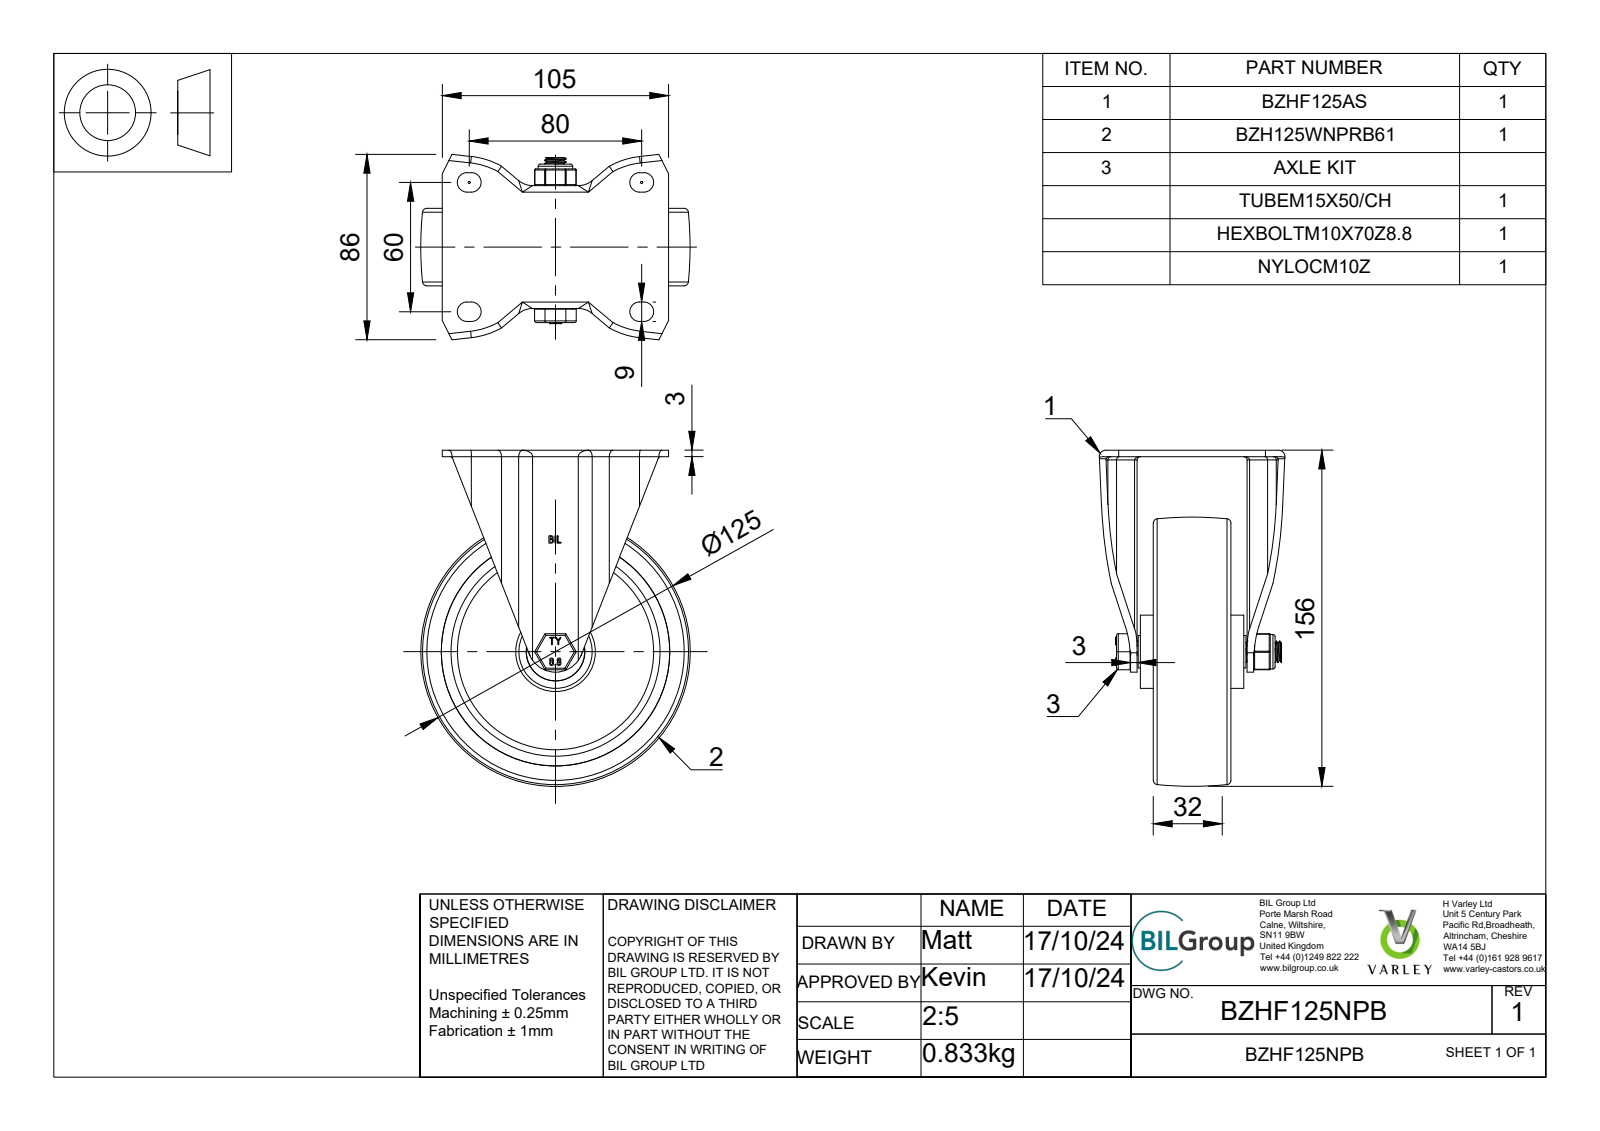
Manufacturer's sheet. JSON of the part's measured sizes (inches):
{"part_name": "BZHF125NPB v3; BZHF125AS v1; ZINC PLATED, PRESSED STEEL BRACKET; BZH125WNPRB61 v1 (+7 more)", "step_written_by": "Autodesk Translation Framework v13.20.0.188 (AUTOMOTIVE_DESIGN)", "units": "inches", "bodies": {"solids": 18, "faces": 470, "planar": 218, "cylindrical": 166, "other": 86}, "overall_size": [6.142, 4.921, 3.386], "volume_in3": 19.06, "surface_area_in2": 213, "round_holes": [[0.394, 1], [0.402, 1], [0.413, 1], [0.472, 1], [0.598, 1], [0.61, 1], [0.925, 1], [1.071, 1], [3.819, 1], [4.173, 1]], "round_bosses_or_shafts": [[0.157, 9], [1.339, 1], [1.063, 1], [0.866, 1], [0.63, 1], [0.591, 1], [0.388, 1], [0.32, 1]], "partial_cylinders_radius": [[0.02, 18], [0.059, 12], [0.118, 10], [0.177, 8], [0.03, 6], [0.197, 4], [0.394, 4], [1.337, 4]], "face_to_face_distances": [0.118, 0.827, 0.591, 0.236, 0.295, 0.886, 1.122, 1.713, 1.831, 1.004]}
